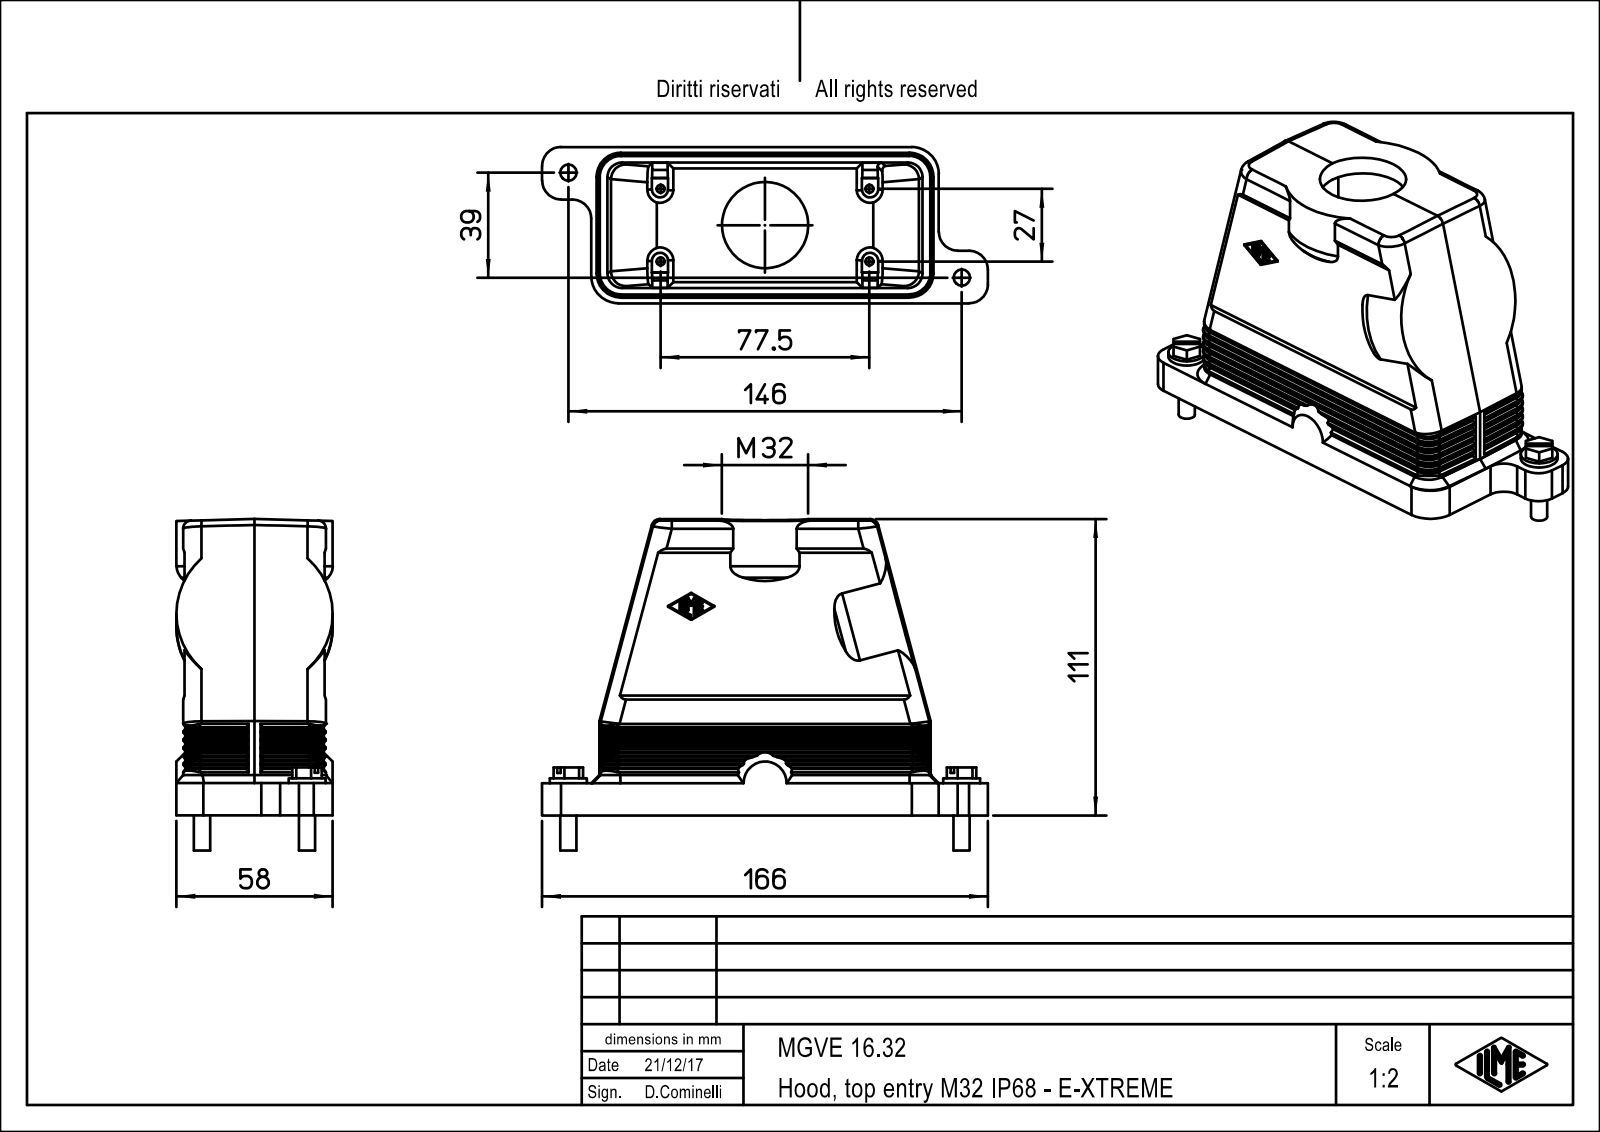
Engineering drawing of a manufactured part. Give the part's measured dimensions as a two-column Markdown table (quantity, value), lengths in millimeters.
| quantity | value |
| --- | --- |
| part name | MGVE_16.32 |
| STEP written by | PTC Creo Elements/Direct Modeling 19.0E 27-Jun-2016 (C) Parametric Technology GmbH (AUTOMOTIVE_DESIGN) |
| units | millimeters |
| bodies | 1 solid, 534 faces (254 planar, 124 cylindrical, 156 other) |
| overall size | 165.5 × 123 × 58 |
| volume | 185 965 mm³ |
| surface area | 84 835 mm² |
| round holes (diameter × count) | 3 × 4, 32 × 1 |
| round bosses / shafts (diameter × count) | 13.7 × 2, 6 × 2 |
| partial cylindrical surfaces (radius × count) | 7 × 62, 0.33 × 15, 5.5 × 8, 8.5 × 4, 0.17 × 2, 10 × 2, 29 × 2, 0.17 × 1 |
| main face-to-face distances | 52, 3, 55, 2.5, 0.5, 55.5, 52.5, 78, 3.33, 1.67 |
| hole center spacings | 41.03, 27, 77.5, 82.07 |
